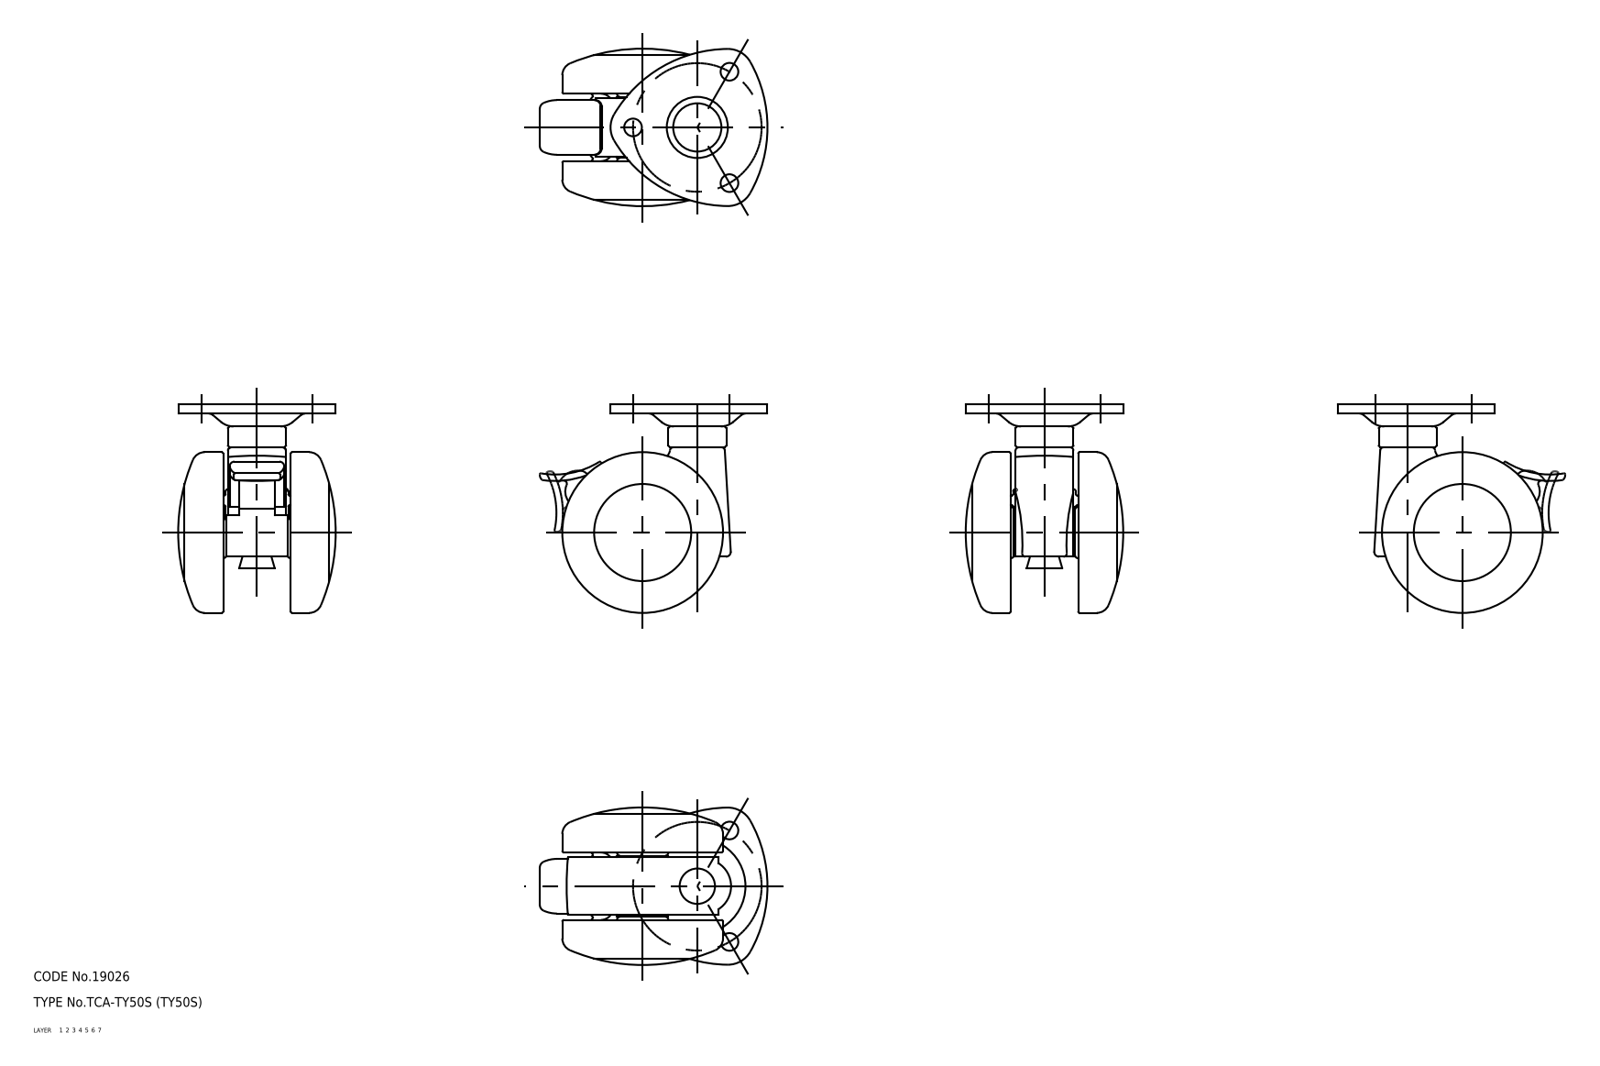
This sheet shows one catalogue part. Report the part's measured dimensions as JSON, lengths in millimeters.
{"part_name": "wheel; mounting plate; main shaft; lever (+1 more)", "step_written_by": "CADfix (AUTOMOTIVE_DESIGN)", "units": "millimeters", "bodies": {"solids": 6, "faces": 227, "planar": 0, "cylindrical": 0, "other": 227}, "overall_size": [70.82, 65, 49], "volume_mm3": 68778, "surface_area_mm2": 31781}
